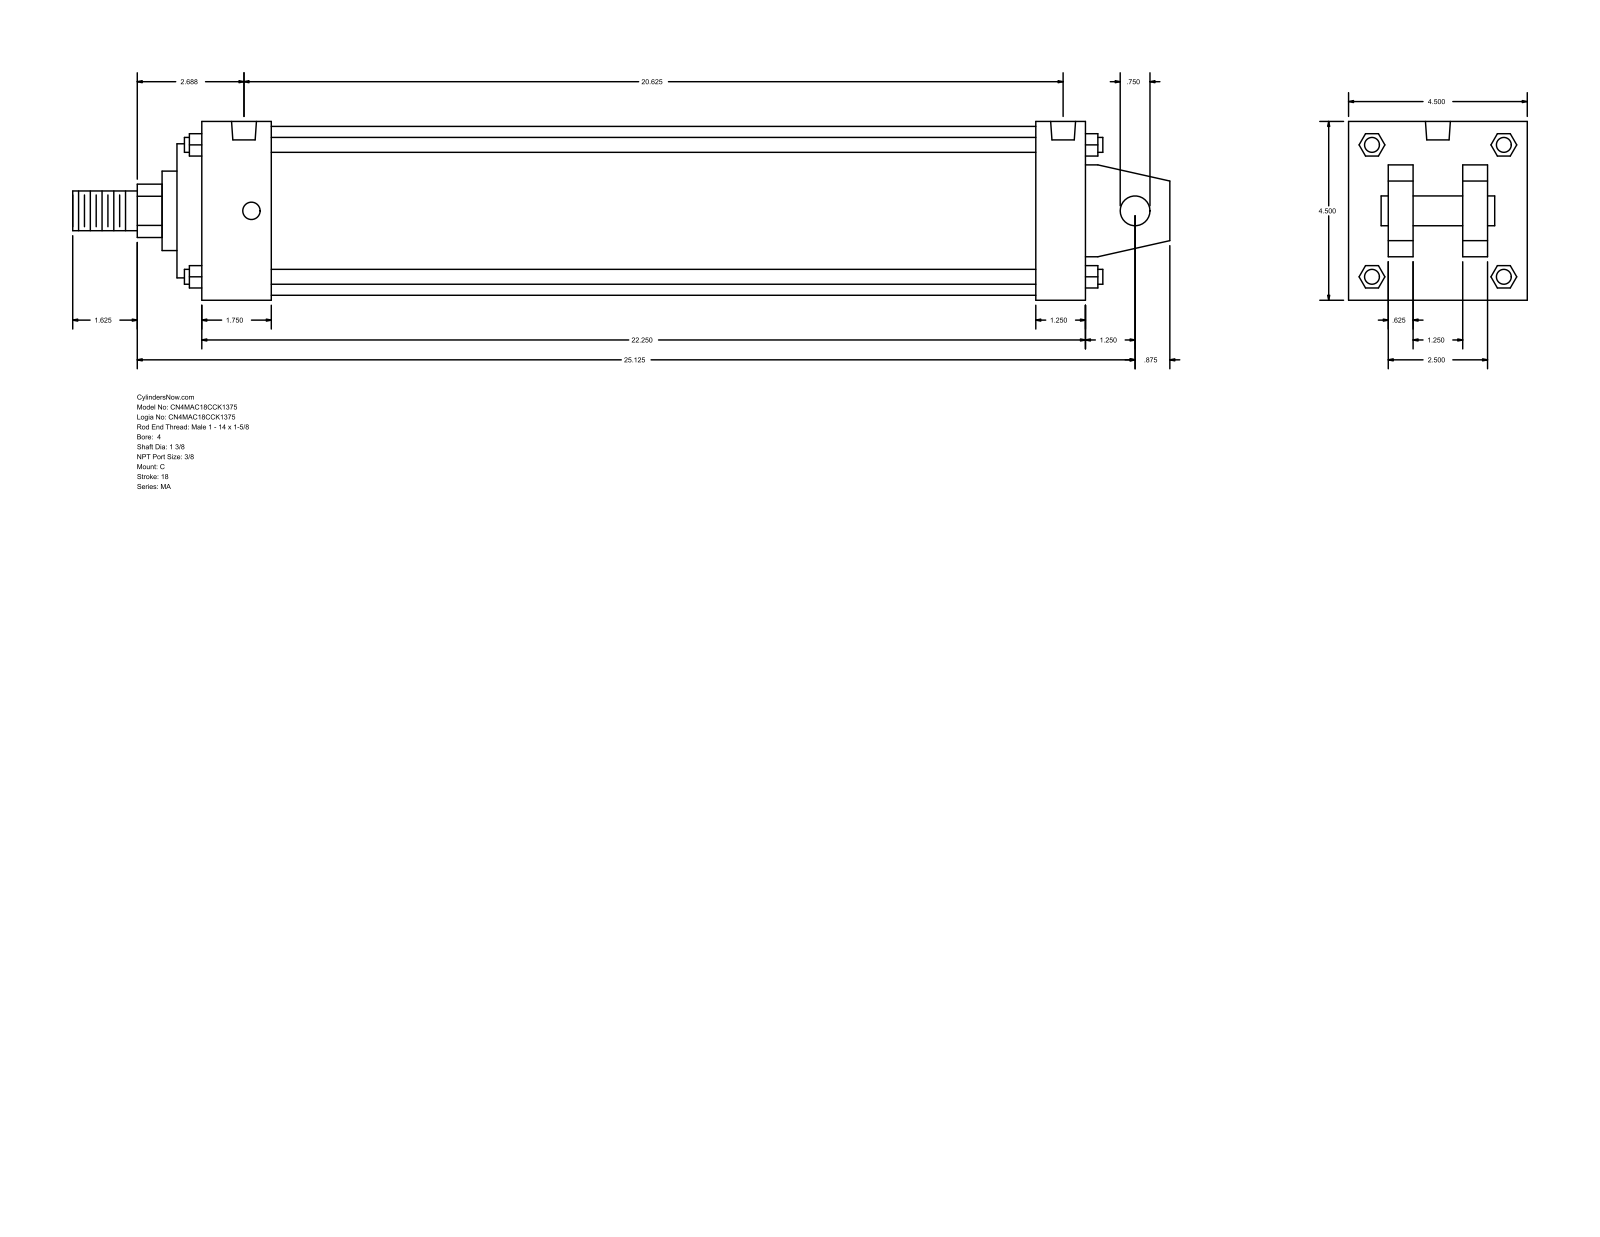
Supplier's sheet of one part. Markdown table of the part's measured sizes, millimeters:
| quantity | value |
| --- | --- |
| part name | MA_C__0400_1.375 |
| STEP written by | GSSL Pune (CONFIG_CONTROL_DESIGN) |
| units | millimeters |
| bodies | 0 solids, 141 faces (109 planar, 32 cylindrical, 0 other) |
| overall size | 701.67 × 114.3 × 114.3 |
| round holes (diameter × count) | 11.11 × 4, 15.93 × 2 |
| round bosses / shafts (diameter × count) | 9.53 × 4, 107.95 × 1, 85.72 × 1, 50.8 × 1, 34.92 × 1, 25.4 × 1, 19.05 × 1 |
| partial cylindrical surfaces (radius × count) | 17.06 × 1 |
| main face-to-face distances | 114.3, 15.87, 565.15, 73.03, 41.27, 25.4, 88.9, 47.63, 581.02, 549.27 |
| hole center spacings | 514.35, 4.76, 4.77, 519.11, 519.12, 523.88 |
